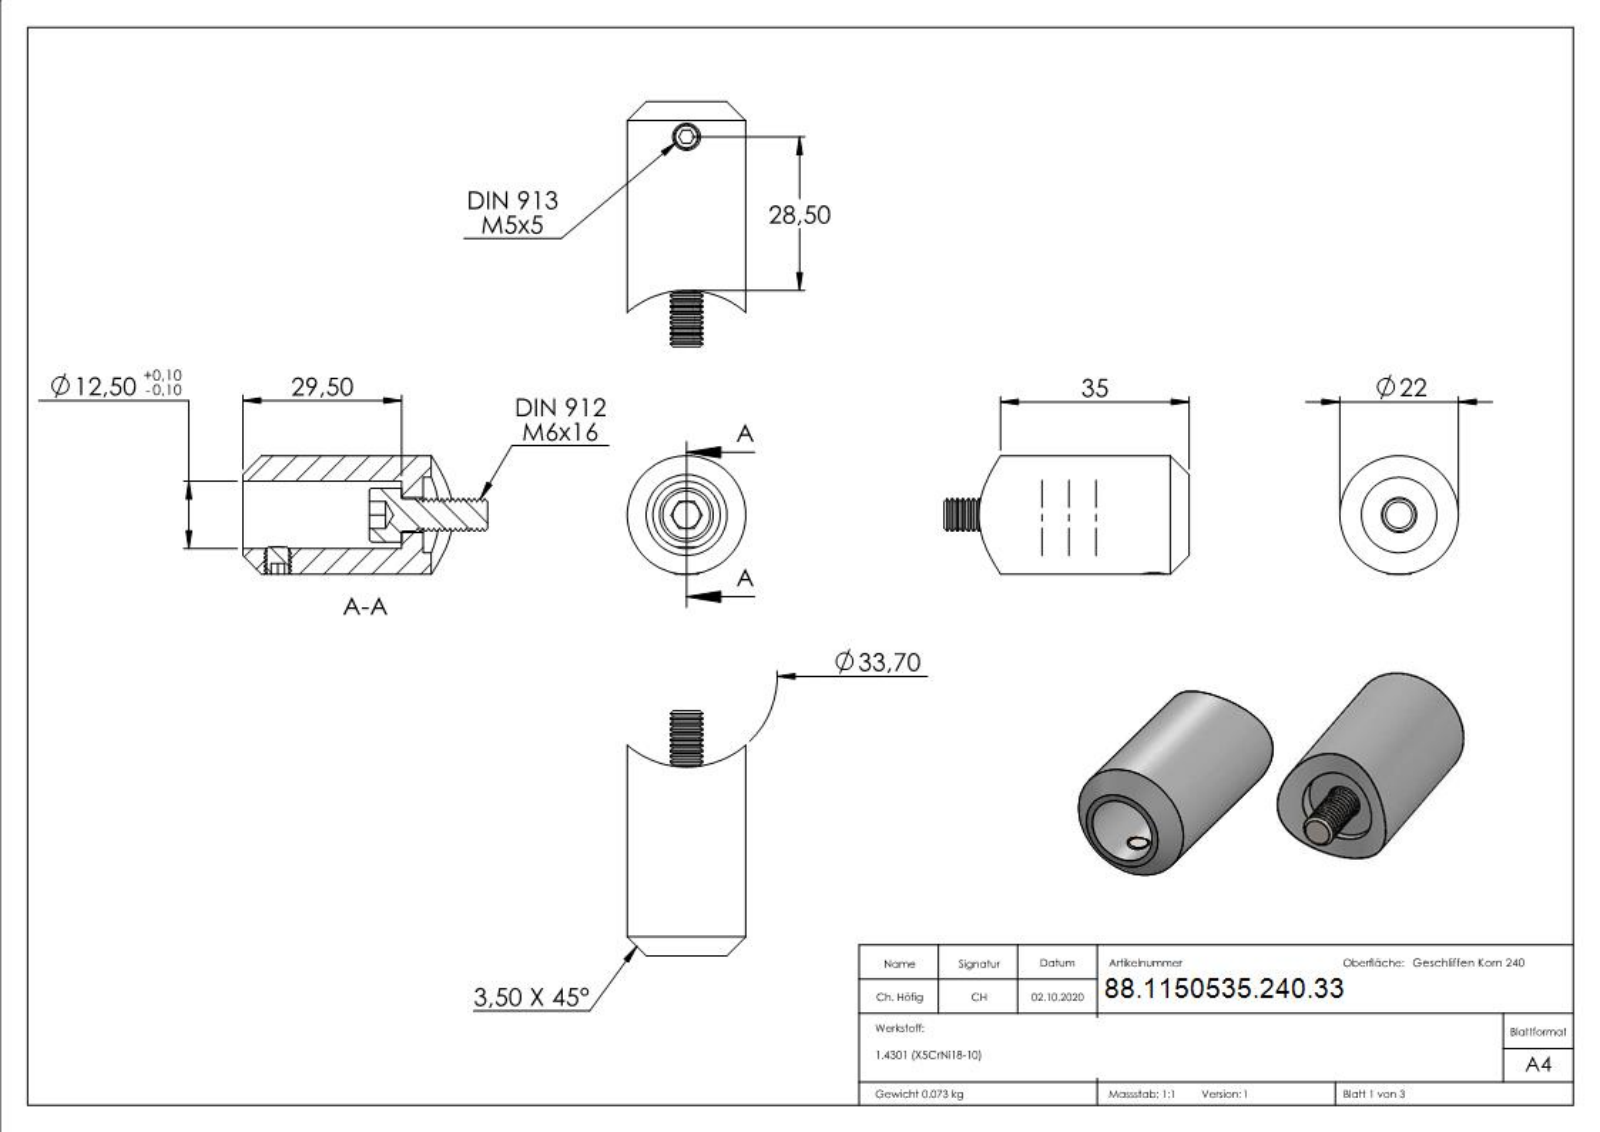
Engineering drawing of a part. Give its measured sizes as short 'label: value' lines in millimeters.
name: socket head cap screw_din; 50535-240-33; socket set screw flat point_din_DIN 913 - M5 x 5-S; socket head cap screw_din_DIN 912 M6 x 16 --- 16S (+3 more)
written by: SolidWorks 2018 (CONFIG_CONTROL_DESIGN)
unit: mm
bodies: 3 solids, 449 faces (155 planar, 64 cylindrical, 230 other)
size: 45.5 × 22 × 22
volume: 10 045 mm³; area: 5 445 mm²
holes: 1× ⌀4.2, 1× ⌀6.5, 1× ⌀12.5, 1× ⌀14
bosses: 1× ⌀22, 1× ⌀10, 1× ⌀6, 1× ⌀5
rounds: 1× R16.85
face distances: 4, 33.5, 29.5, 6, 10, 23.5, 5.02, 12, 16, 22
